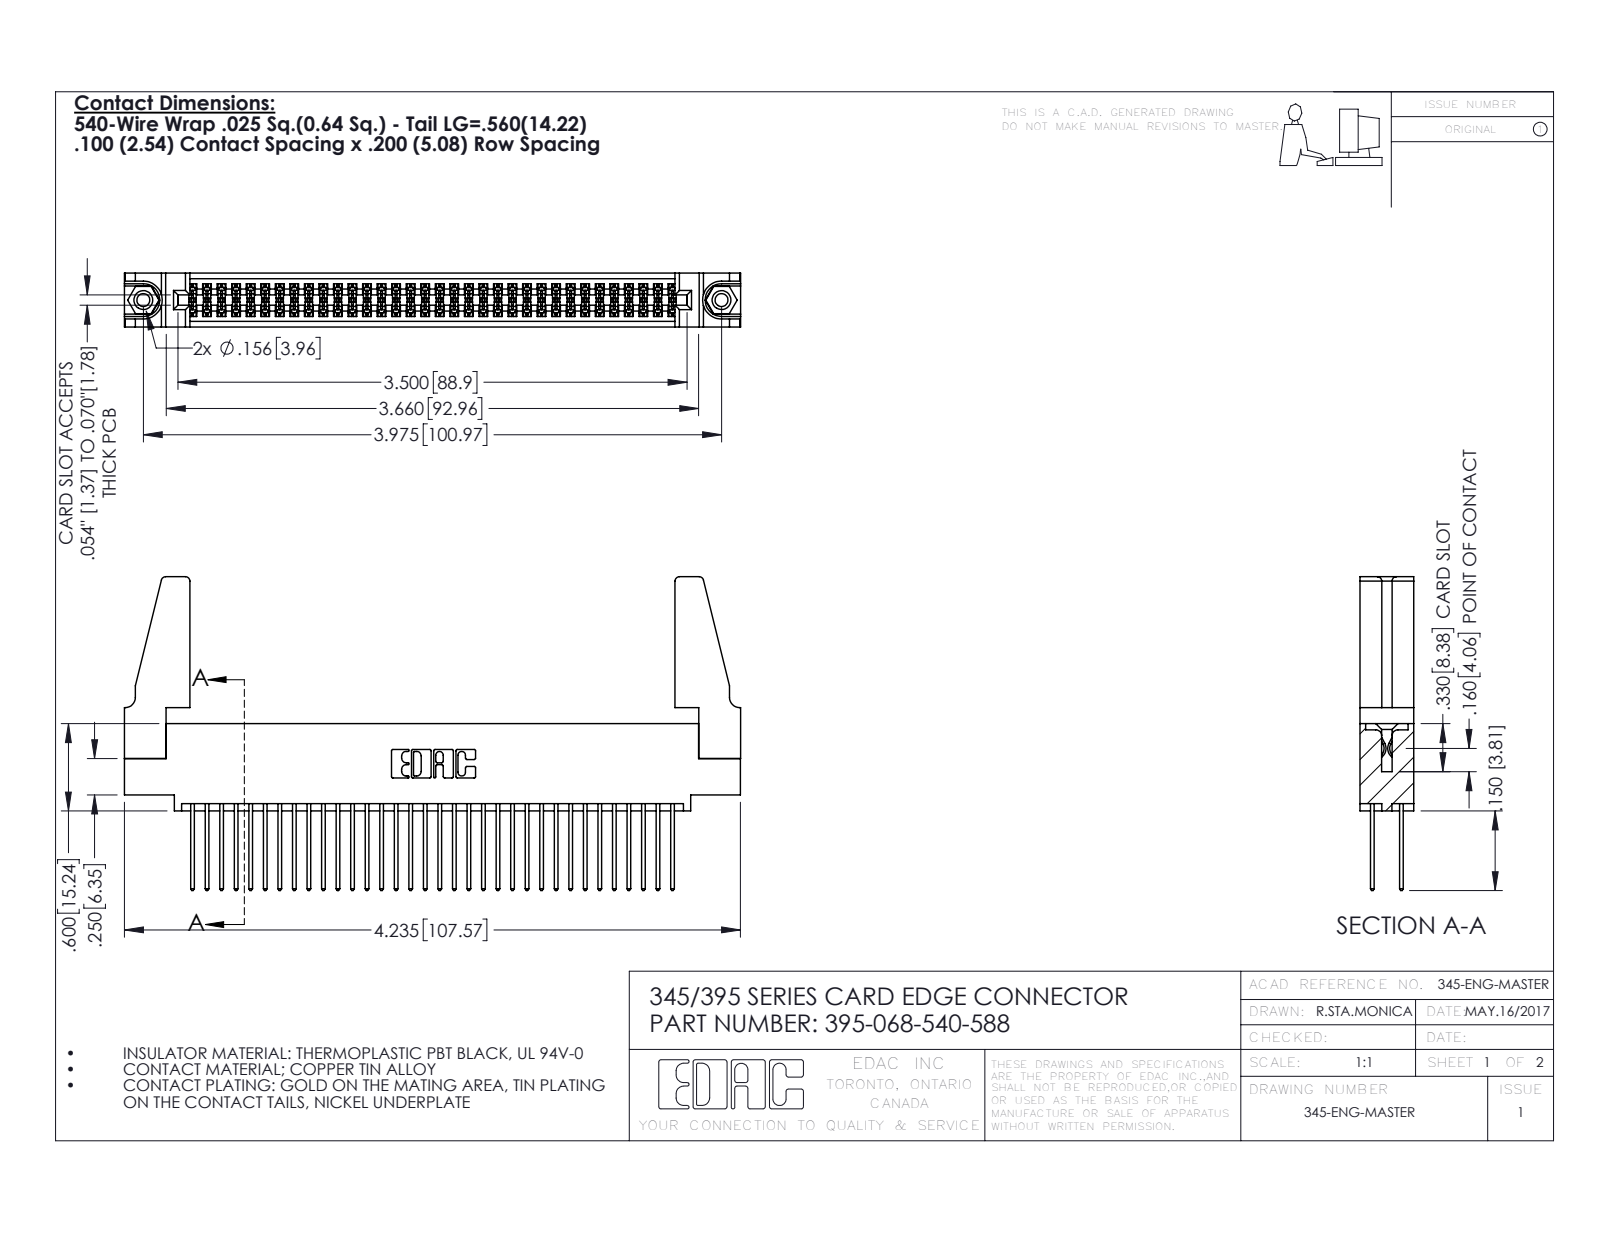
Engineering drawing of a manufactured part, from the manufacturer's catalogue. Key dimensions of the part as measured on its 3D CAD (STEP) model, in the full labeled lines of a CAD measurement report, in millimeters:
Part name (STEP PRODUCT): 345-220-078_345-220-088; 345-292-001_345-293-140; 395-068-540-588; 345 Part_0.110 Offset - 0.156 Dia-TH (+1 more)
STEP written by: SolidWorks 2016 (CONFIG_CONTROL_DESIGN)
Units: millimetres
Bodies: 73 solids, 3654 faces (2400 planar, 1238 cylindrical, 16 other)
Overall size (bounding box): 107.6 × 54.8 × 9.4
Volume: 13 800 mm³ · Surface area: 19 870 mm²
Round holes (diameter × count): ⌀2.3 ×2, ⌀3.2 ×2, ⌀4 ×2, ⌀1.6 ×1
Round bosses / shafts (diameter × count): ⌀3.9 ×2
Partial cylindrical surfaces — rounded edges, fillets, slot ends (radius × count): R0.2 ×102, R0.3 ×68, R0.3 ×22, R0.8 ×8, R0.2 ×6, R0.8 ×6, R0.7 ×3, R0.4 ×2
Main face-to-face distances: 1.8, 7.6, 9.4, 5.1, 2.5, 6.9, 0.6, 5.7, 4.4, 3.8
Hole centre spacings: 6.9, 95, 101
